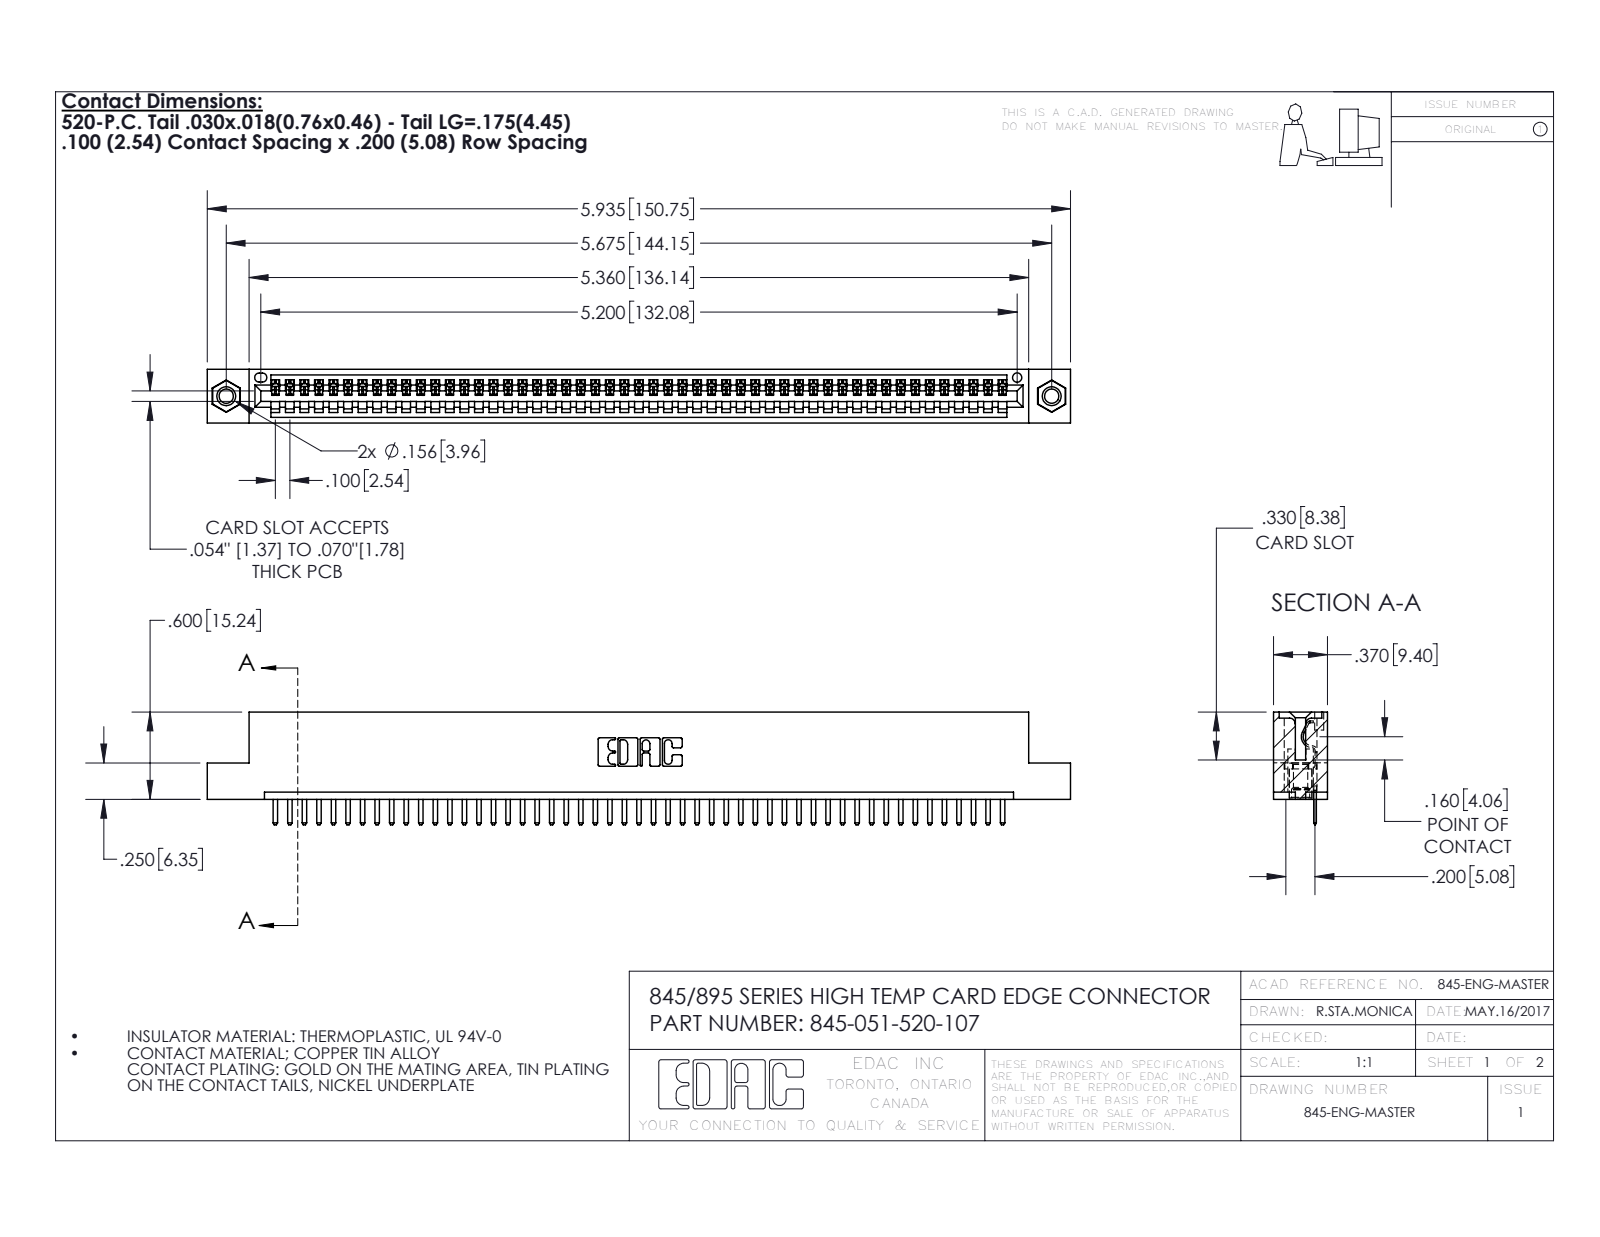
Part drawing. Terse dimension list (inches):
name: 345-292-001_345-293-120; 345-051-520-107; 345 Part_Flush Mounting Lugs - 0.156 Dia-TI; 345-250-001_345-250-005-103
written by: SolidWorks 2016 (CONFIG_CONTROL_DESIGN)
unit: in
bodies: 54 solids, 3348 faces (2254 planar, 1078 cylindrical, 16 other)
size: 5.935 × 0.775 × 0.37
volume: 0.868 in³; area: 28.81 in²
holes: 2× ⌀0.098, 2× ⌀0.125, 2× ⌀0.156, 1× ⌀0.064
bosses: 2× ⌀0.155
rounds: 104× R0.01, 102× R0.006, 22× R0.01, 6× R0.007, 6× R0.031, 3× R0.026, 2× R0.031, 2× R0.04
face distances: 0.072, 0.298, 0.37, 0.2, 0.098, 0.272, 0.025, 0.225, 0.072, 0.149
hole spacings: 0.27, 5.439, 5.675
